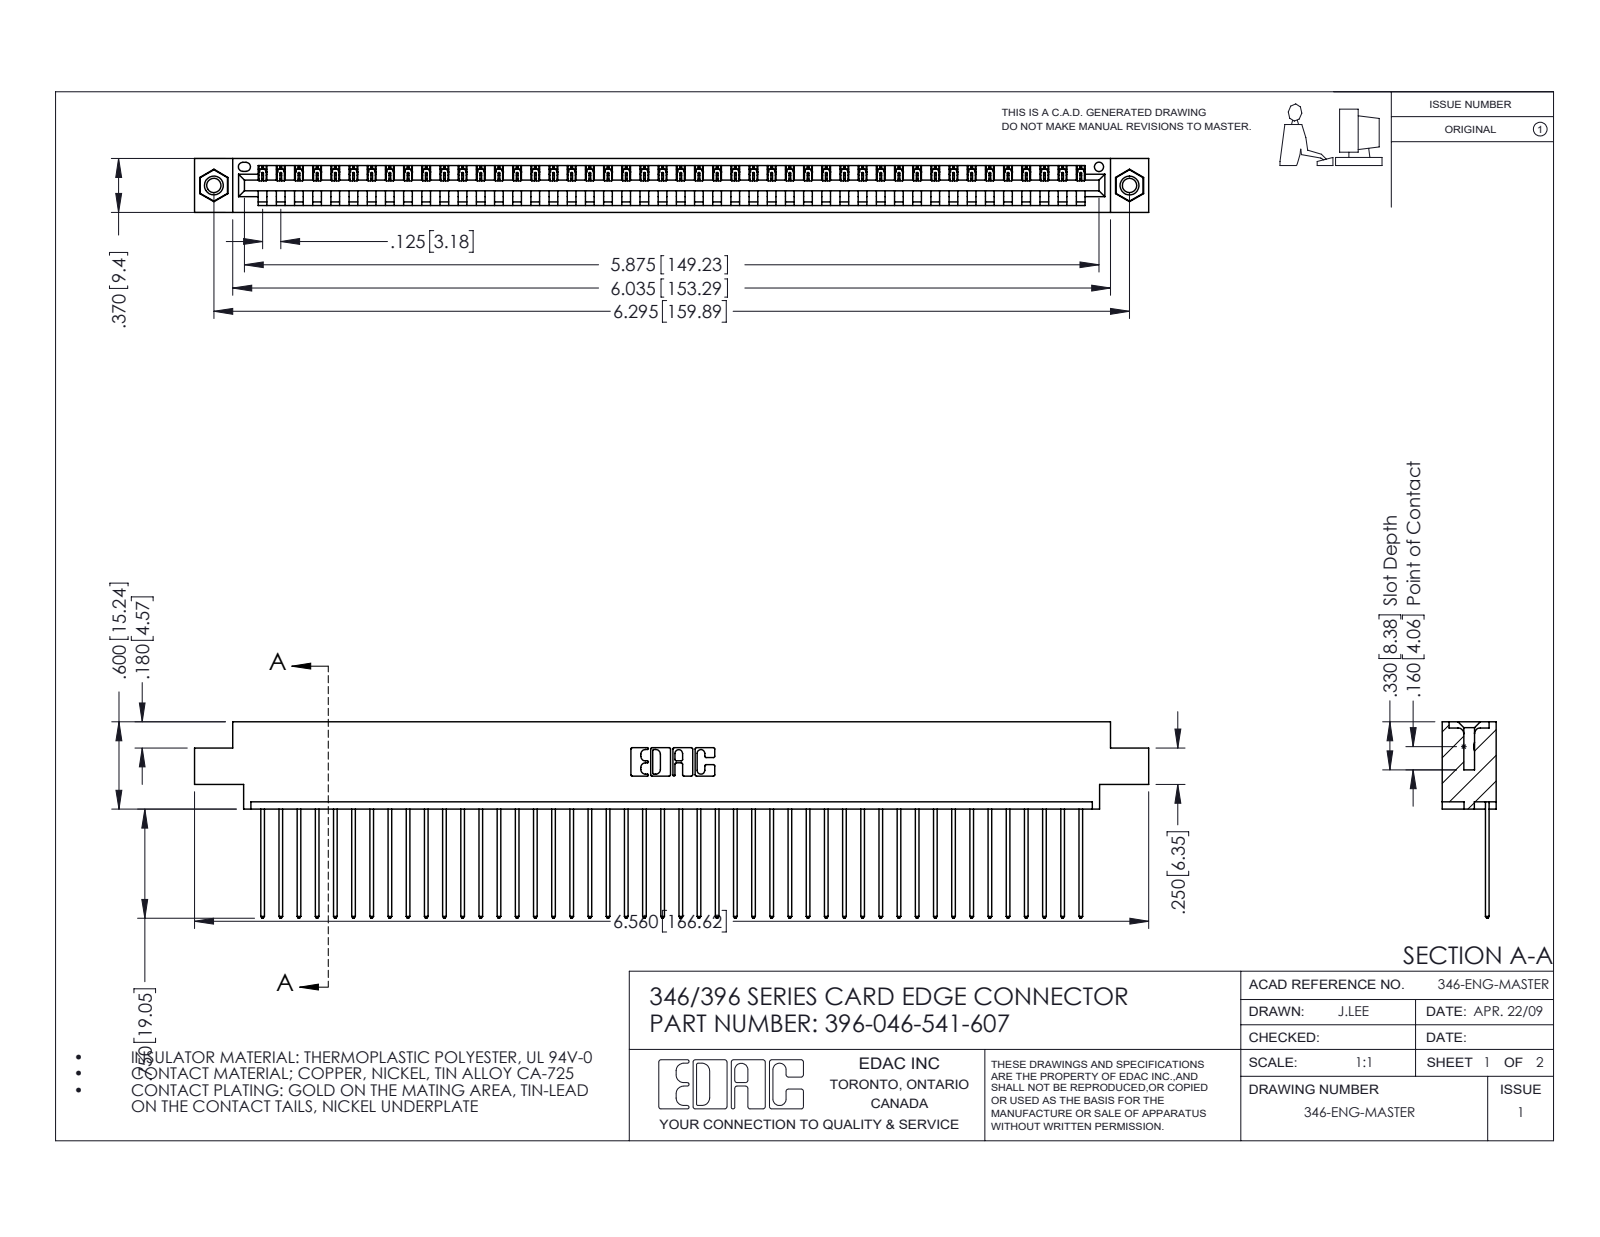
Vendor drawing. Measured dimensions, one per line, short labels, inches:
name: 345-250-001_345-250-005-103; 345-292-001_345-293-141; 396-046-541-607; 346 Part_0.170 Offset - 0.156 Dia-TI
written by: SolidWorks 2016 (CONFIG_CONTROL_DESIGN)
unit: in
bodies: 49 solids, 2854 faces (1952 planar, 886 cylindrical, 16 other)
size: 6.56 × 1.35 × 0.37
volume: 0.974 in³; area: 32.7 in²
holes: 2× ⌀0.098, 2× ⌀0.125, 2× ⌀0.156, 1× ⌀0.064
bosses: 2× ⌀0.155
rounds: 92× R0.006, 92× R0.01, 22× R0.01, 6× R0.007, 6× R0.031, 3× R0.026, 2× R0.031, 2× R0.04
face distances: 0.048, 0.322, 0.37, 0.25, 0.072, 0.298, 0.025, 0.222, 0.148, 0.1
hole spacings: 0.246, 6.086, 6.295
